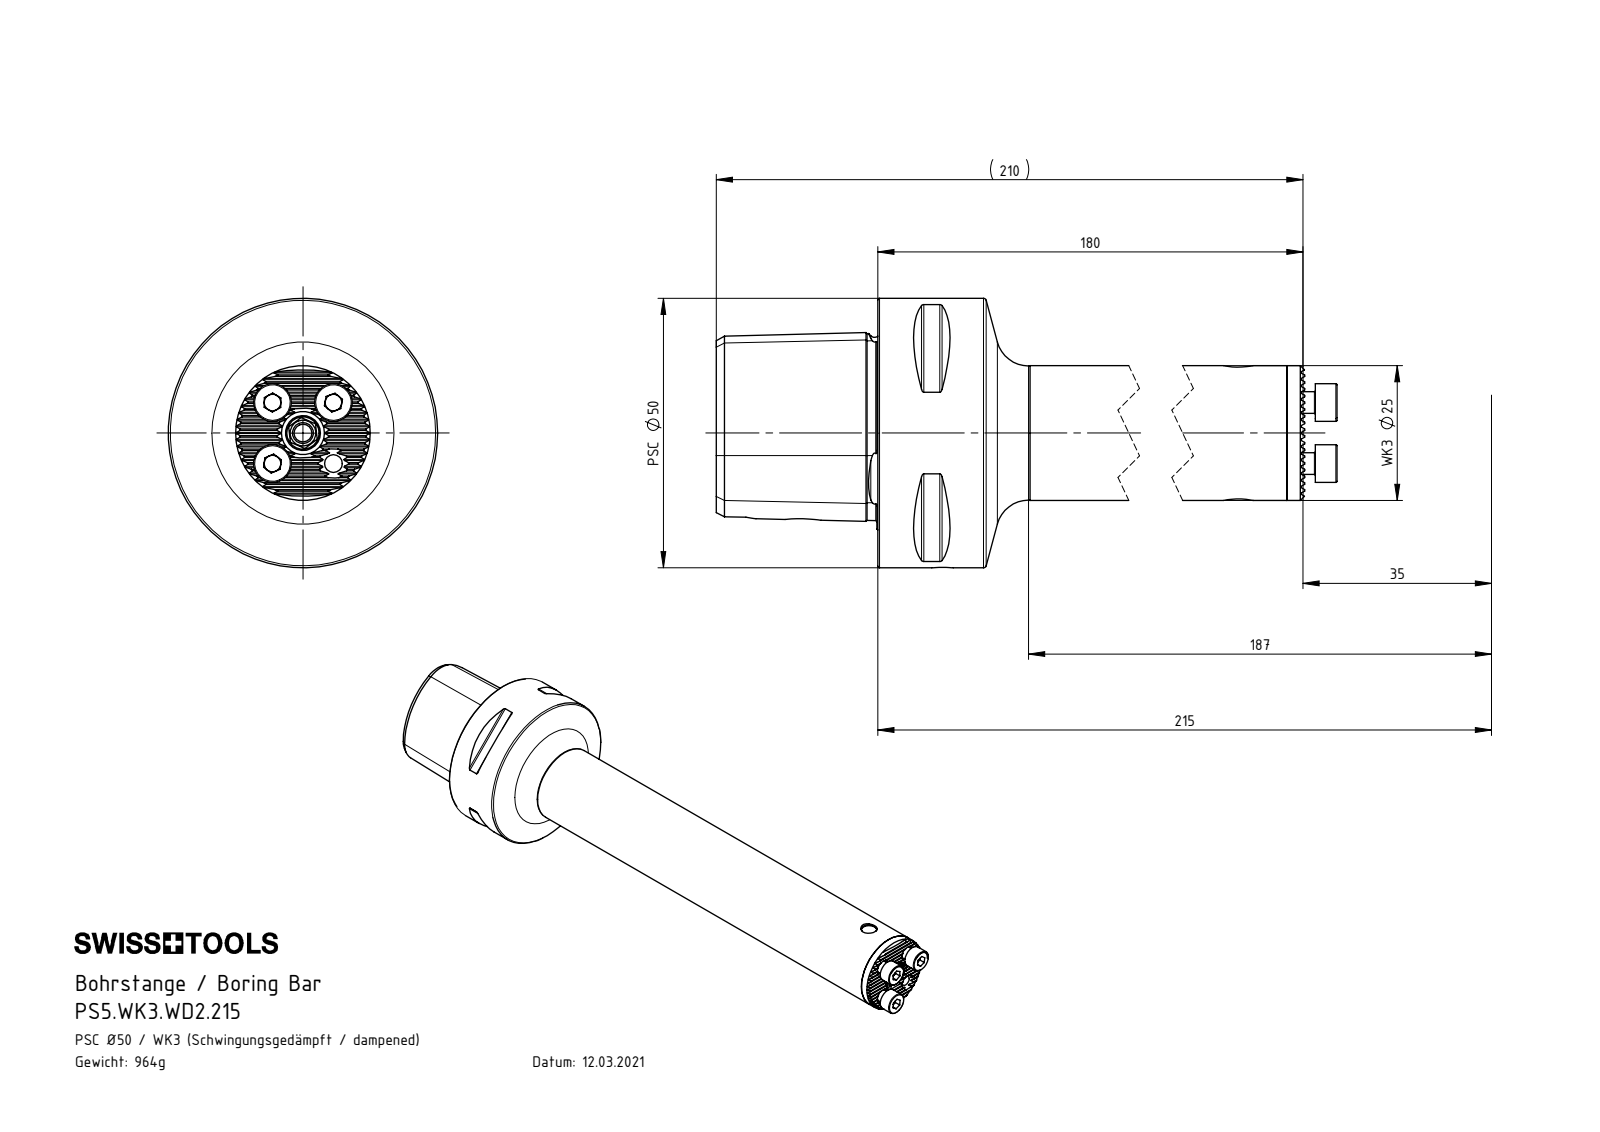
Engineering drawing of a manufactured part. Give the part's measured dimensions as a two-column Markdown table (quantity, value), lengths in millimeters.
| quantity | value |
| --- | --- |
| part name | WD2-BG1.021.085; DIN 6325_ø5x10-m6_2x6; DIN 3771 - 17x2; ISO 4762 - M4 x 12 (+8 more) |
| STEP written by | SolidWorks 2017 (AUTOMOTIVE_DESIGN) |
| units | millimeters |
| bodies | 16 solids, 491 faces (236 planar, 110 cylindrical, 145 other) |
| overall size | 216.3 × 50 × 50 |
| volume | 125 731 mm³ |
| surface area | 53 004 mm² |
| round holes (diameter × count) | 3.3 × 5, 4 × 1, 5 × 1, 5.5 × 1, 6 × 1, 6.1 × 1, 6.5 × 1, 6.8 × 1, 7.4 × 1, 8.5 × 1, 9 × 1, 11 × 1 |
| round bosses / shafts (diameter × count) | 7 × 3, 4 × 3, 50 × 1, 25 × 1, 21 × 1, 20.7 × 1, 20 × 1, 17.8 × 1 |
| partial cylindrical surfaces (radius × count) | 0.12 × 19, 0.5 × 8, 4 × 1 |
| main face-to-face distances | 6, 78.4, 30, 3.2, 75.2, 75.95, 4.33, 191, 161, 1.08 |
| hole center spacings | 8, 11.32, 16.01, 26, 156, 182 |
